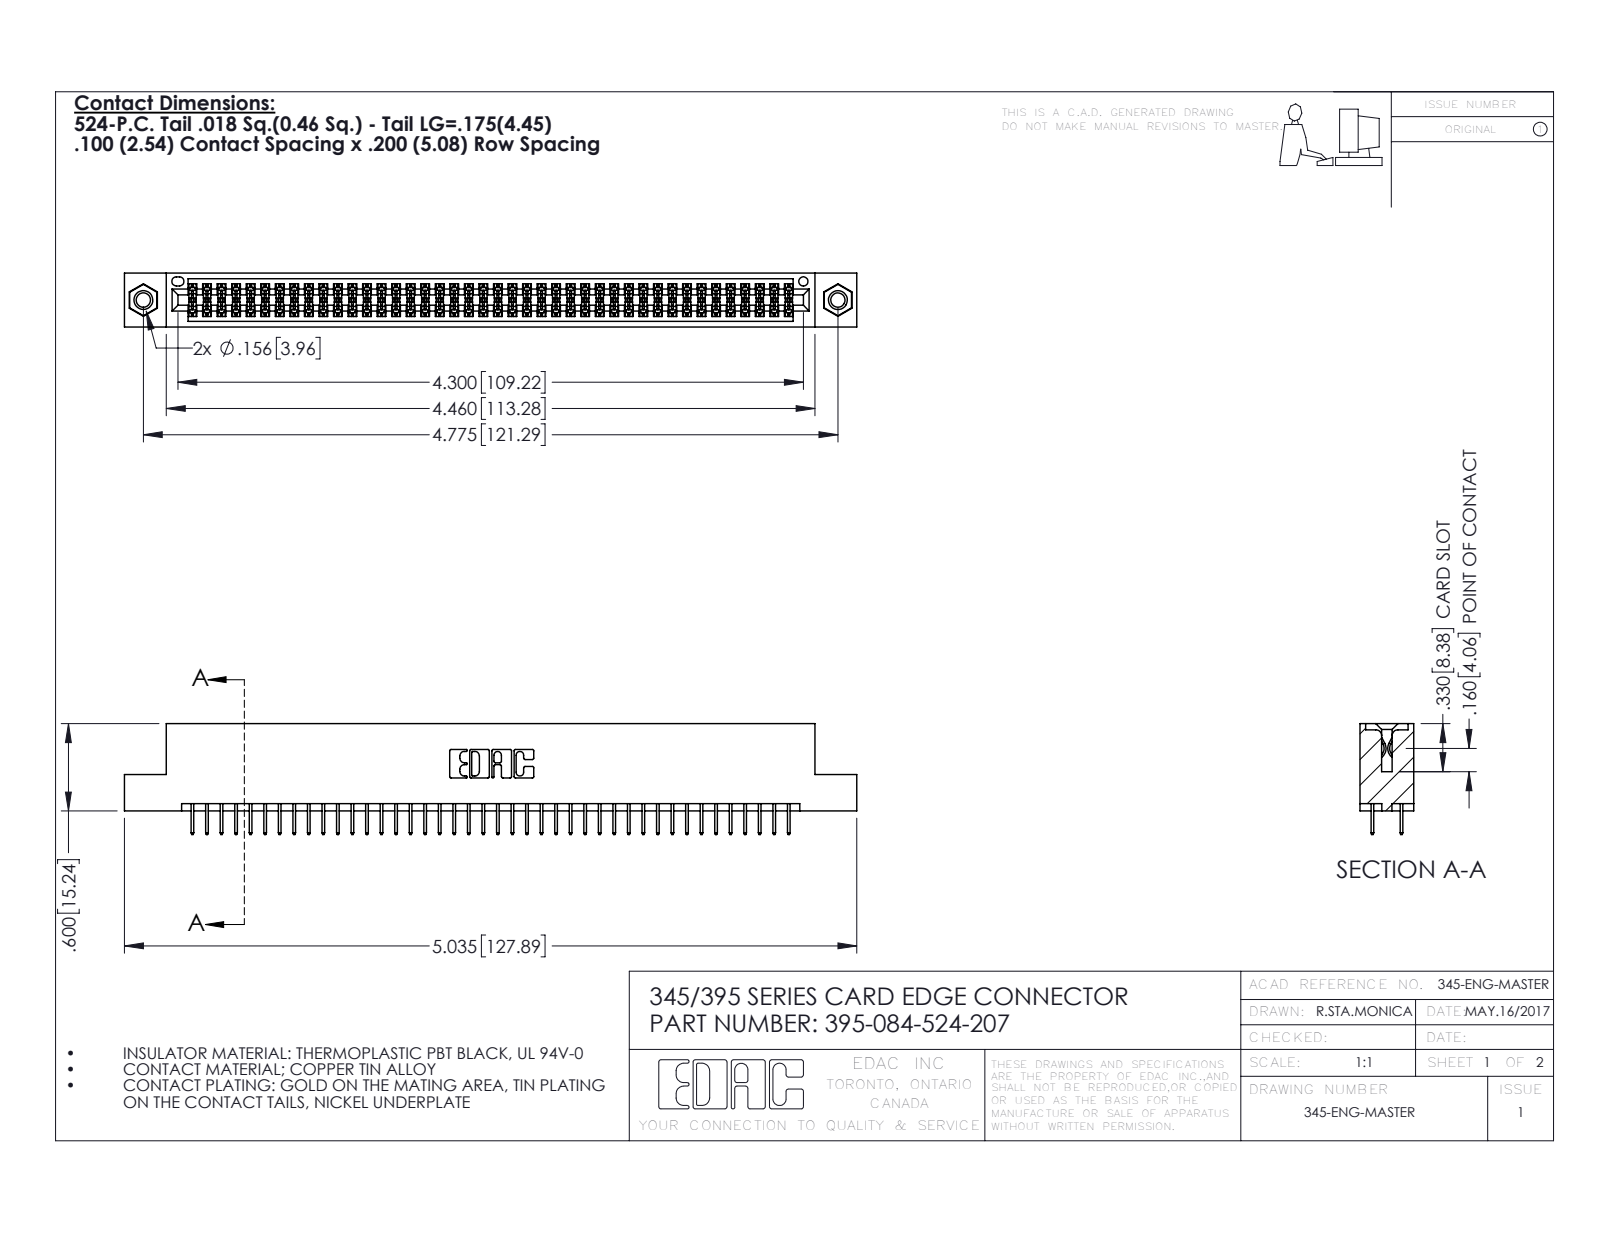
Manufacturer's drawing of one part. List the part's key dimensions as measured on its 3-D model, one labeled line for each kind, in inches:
Part name (STEP PRODUCT): 345-250-001_345-250-005-103; 395-084-524-207; 345-292-001_345-293-124; 345 Part_Flush Mounting Lugs - 0.156 Dia-TI
STEP written by: SolidWorks 2016 (CONFIG_CONTROL_DESIGN)
Units: inches
Bodies: 87 solids, 4722 faces (3388 planar, 1318 cylindrical, 16 other)
Overall size (bounding box): 5.035 × 0.762 × 0.37
Volume: 0.75 in³ · Surface area: 27.66 in²
Round holes (diameter × count): ⌀0.098 ×2, ⌀0.125 ×2, ⌀0.156 ×2, ⌀0.064 ×1
Round bosses / shafts (diameter × count): ⌀0.155 ×2
Partial cylindrical surfaces — rounded edges, fillets, slot ends (radius × count): R0.006 ×126, R0.01 ×22, R0.007 ×6, R0.031 ×6, R0.026 ×3, R0.014 ×2, R0.019 ×2, R0.022 ×2
Main face-to-face distances: 0.072, 0.298, 0.2, 0.37, 0.098, 0.272, 0.025, 0.225, 0.072, 0.175
Hole centre spacings: 0.27, 4.539, 4.775
